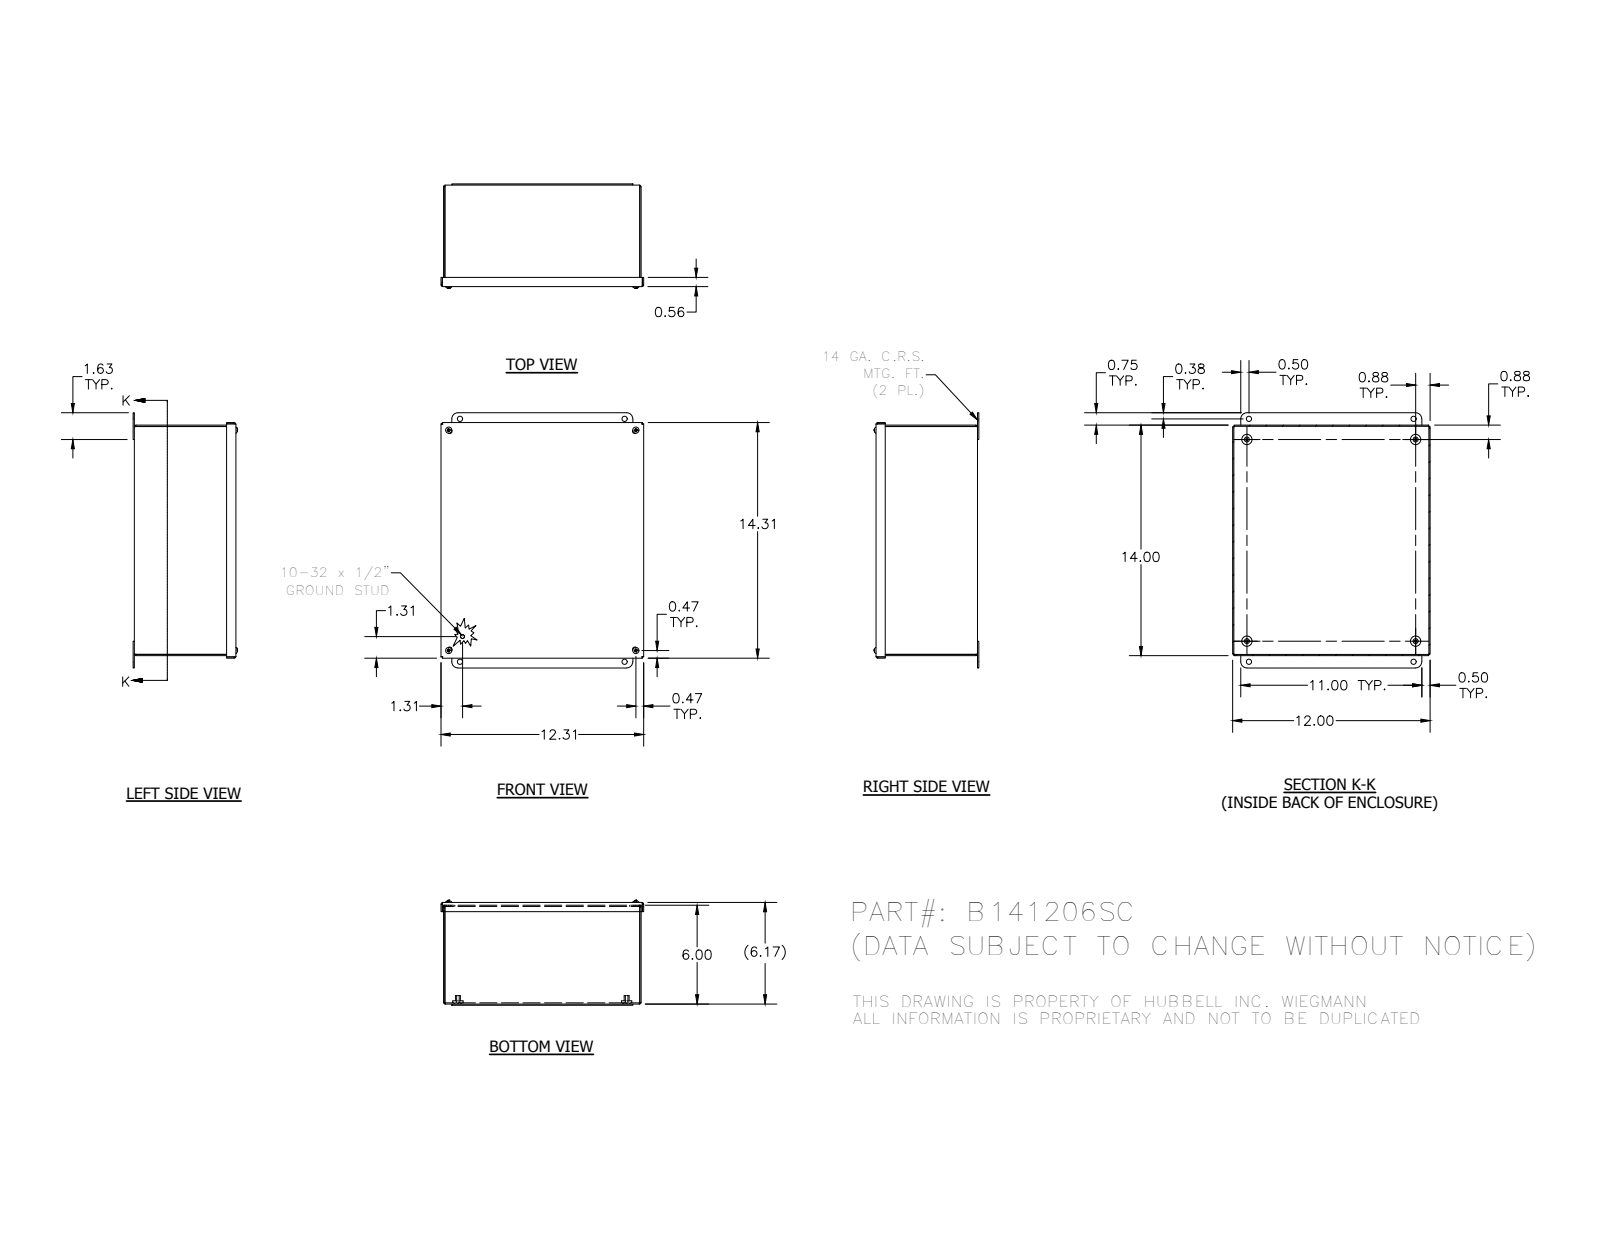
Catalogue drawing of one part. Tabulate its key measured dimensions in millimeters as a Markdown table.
| quantity | value |
| --- | --- |
| part name | B141206SC; 3485; 34984; B141206SCBKP (+6 more) |
| STEP written by | Autodesk Inventor 2012 (AUTOMOTIVE_DESIGN) |
| units | millimeters |
| bodies | 23 solids, 532 faces (311 planar, 102 cylindrical, 119 other) |
| overall size | 393.7 × 312.8 × 161.2 |
| volume | 990 800 mm³ |
| surface area | 1 005 000 mm² |
| round holes (diameter × count) | 3.7 × 4, 4 × 4, 5 × 4, 7.1 × 4, 7.1 × 4, 7.9 × 4, 8 × 4 |
| round bosses / shafts (diameter × count) | 4.8 × 5, 15.9 × 4, 11.5 × 4, 10.3 × 4, 9.5 × 4, 7.6 × 4, 6.3 × 4, 6.4 × 1 |
| partial cylindrical surfaces (radius × count) | 0.8 × 12, 2.7 × 12, 2.3 × 4, 9.5 × 4 |
| main face-to-face distances | 1.9, 154.8, 156.7, 152.9, 302.9, 353.7, 301, 304.8, 355.6, 351.8 |
| hole center spacings | 272, 287.4, 338.2, 340.2, 2.2, 24.7, 338.7, 357.6 |
